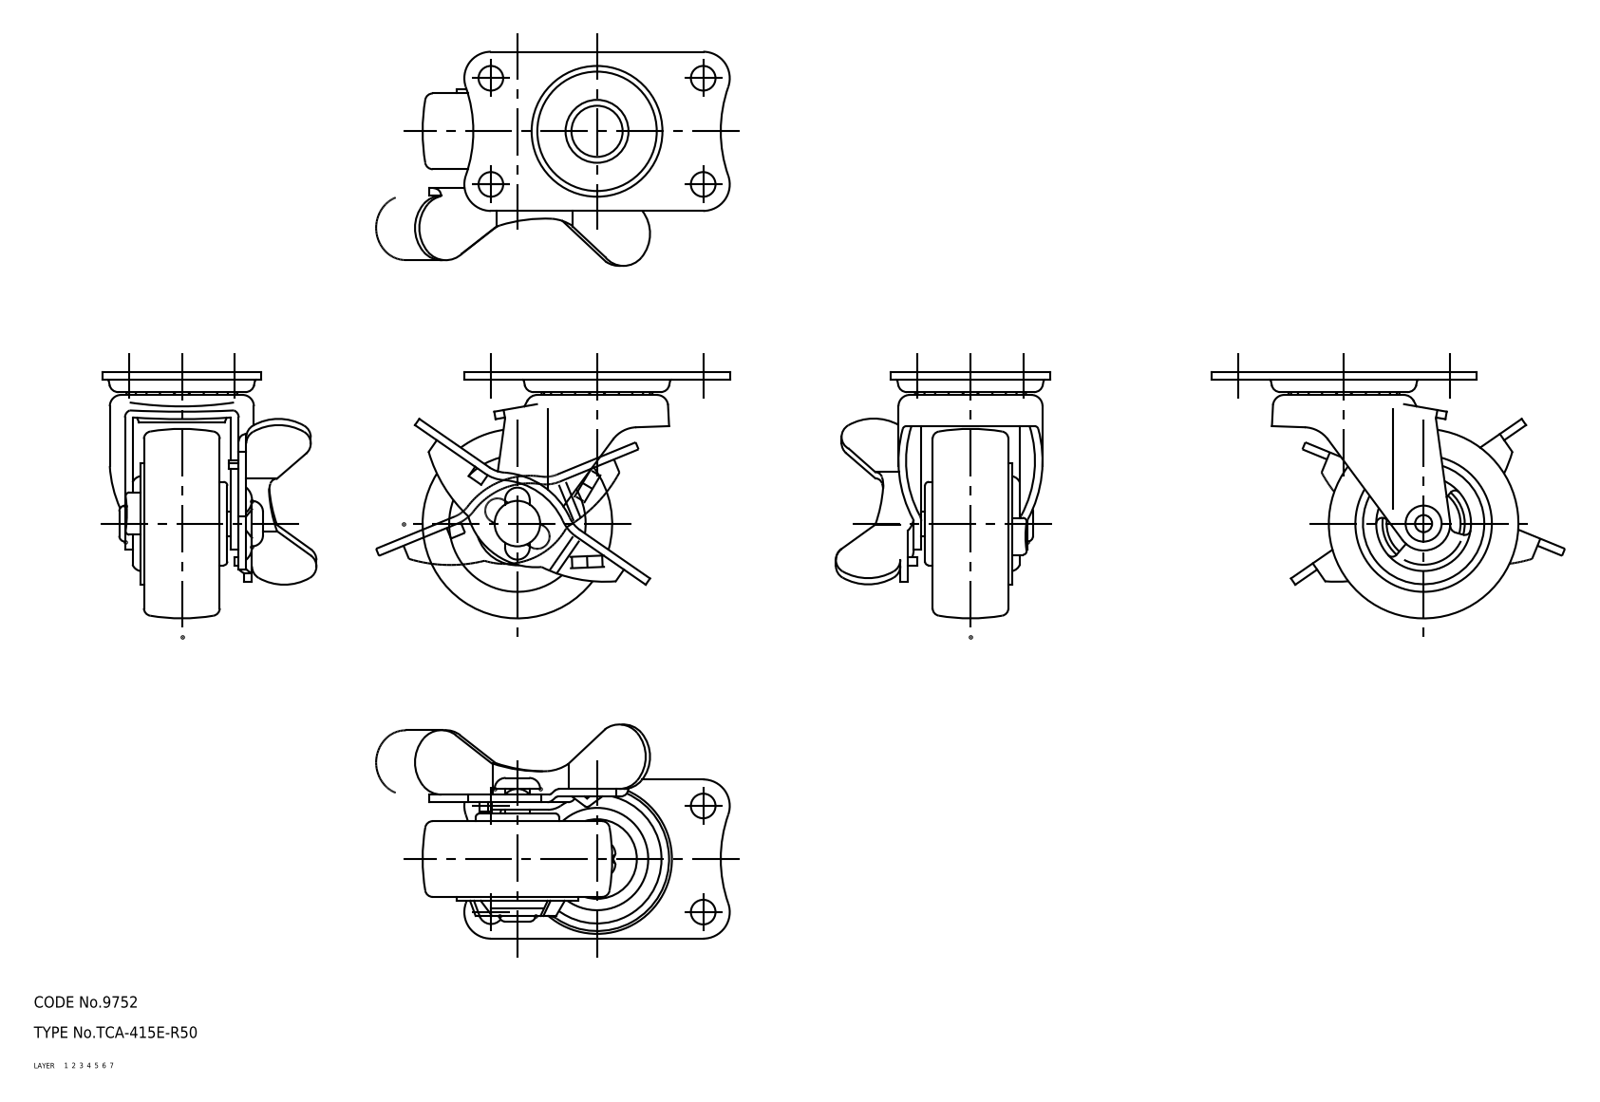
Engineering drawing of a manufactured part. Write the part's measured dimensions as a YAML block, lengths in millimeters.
part_name: "wheel; mounting plate; main shaft; lever (+2 more)"
step_written_by: "CADfix (AUTOMOTIVE_DESIGN)"
units: millimeters
bodies: {solids: 6, faces: 368, planar: 0, cylindrical: 0, other: 368}
overall_size: [83.01, 65, 56.5]
volume: 60822
surface_area: 29577
